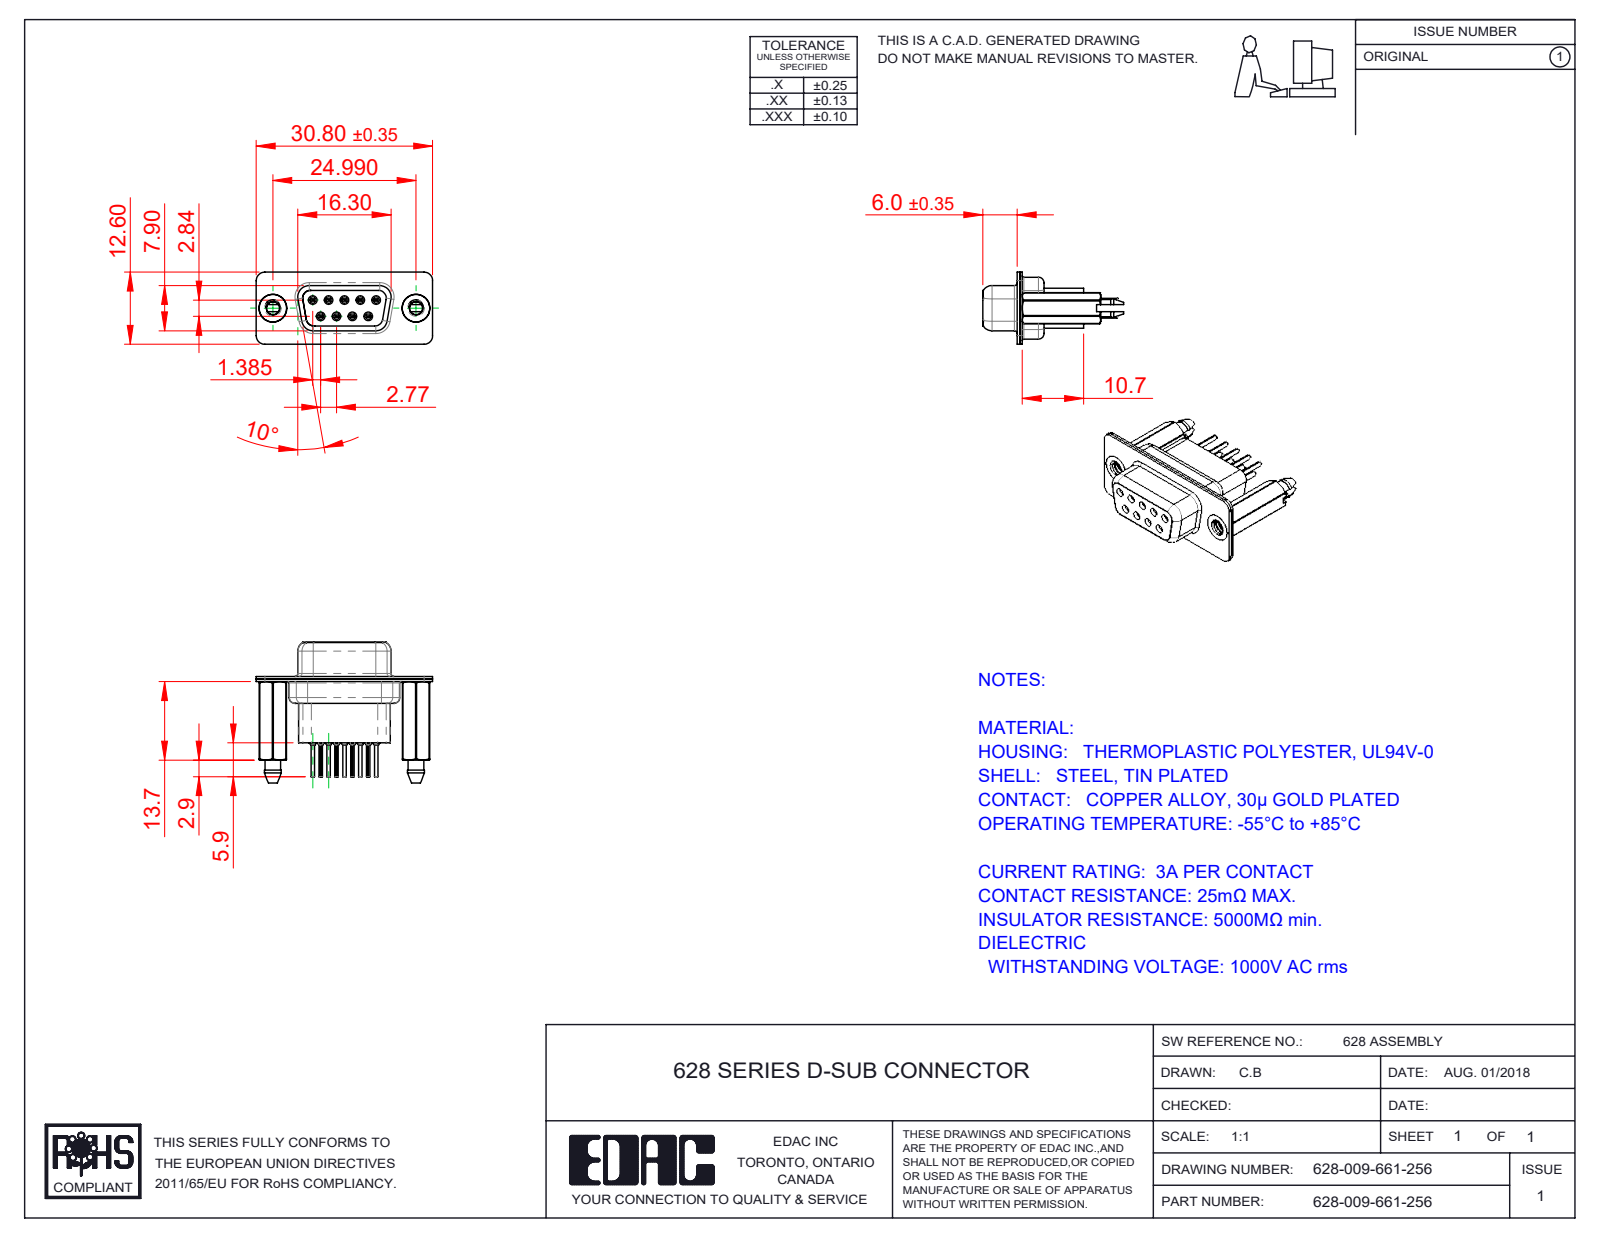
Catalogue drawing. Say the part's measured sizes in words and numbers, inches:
The part is named "628-009-661-256; 628 Shell Rear_09 Contacts; 628 Shell Front_09 Contacts; 628 Contact Row 2_61 (+3 more)". Its 3-D file was written by "SolidWorks 2020 (CONFIG_CONTROL_DESIGN)". It is 14 solids with 1460 faces: 378 planar, 466 cylindrical and 616 other. Overall it measures 1.213 by 0.969 by 0.496 inches. Its volume is 0.158 cubic inches and its surface area 9.345 square inches. Round holes: 9 of diameter 0.008, 9 of diameter 0.031, 9 of diameter 0.035, 9 of diameter 0.043, 9 of diameter 0.063, 5 of diameter 0.067, 2 of diameter 0.089, 2 of diameter 0.157, 2 of diameter 0.159, 2 of diameter 0.191. Round bosses or shafts: 9 of diameter 0.079, 9 of diameter 0.059, 9 of diameter 0.047, 9 of diameter 0.024, 2 of diameter 0.195, 2 of diameter 0.189. Partial cylindrical surfaces (rounded edges, fillets, slot ends): 19 of radius 0.059, 18 of radius 0.004, 12 of radius 0.079, 9 of radius 0.011, 6 of radius 0.053, 6 of radius 0.063, 4 of radius 0.01, 4 of radius 0.02. The main face-to-face distances are 0.018, 0.016, 0.035, 0.335, 0.26, 0.075, 0.055, 0.187, 0.276, 0.421. The hole center spacings are 0.124, 0.109, 0.218, 0.198, 0.198, 0.327, 0.294, 0.295.
